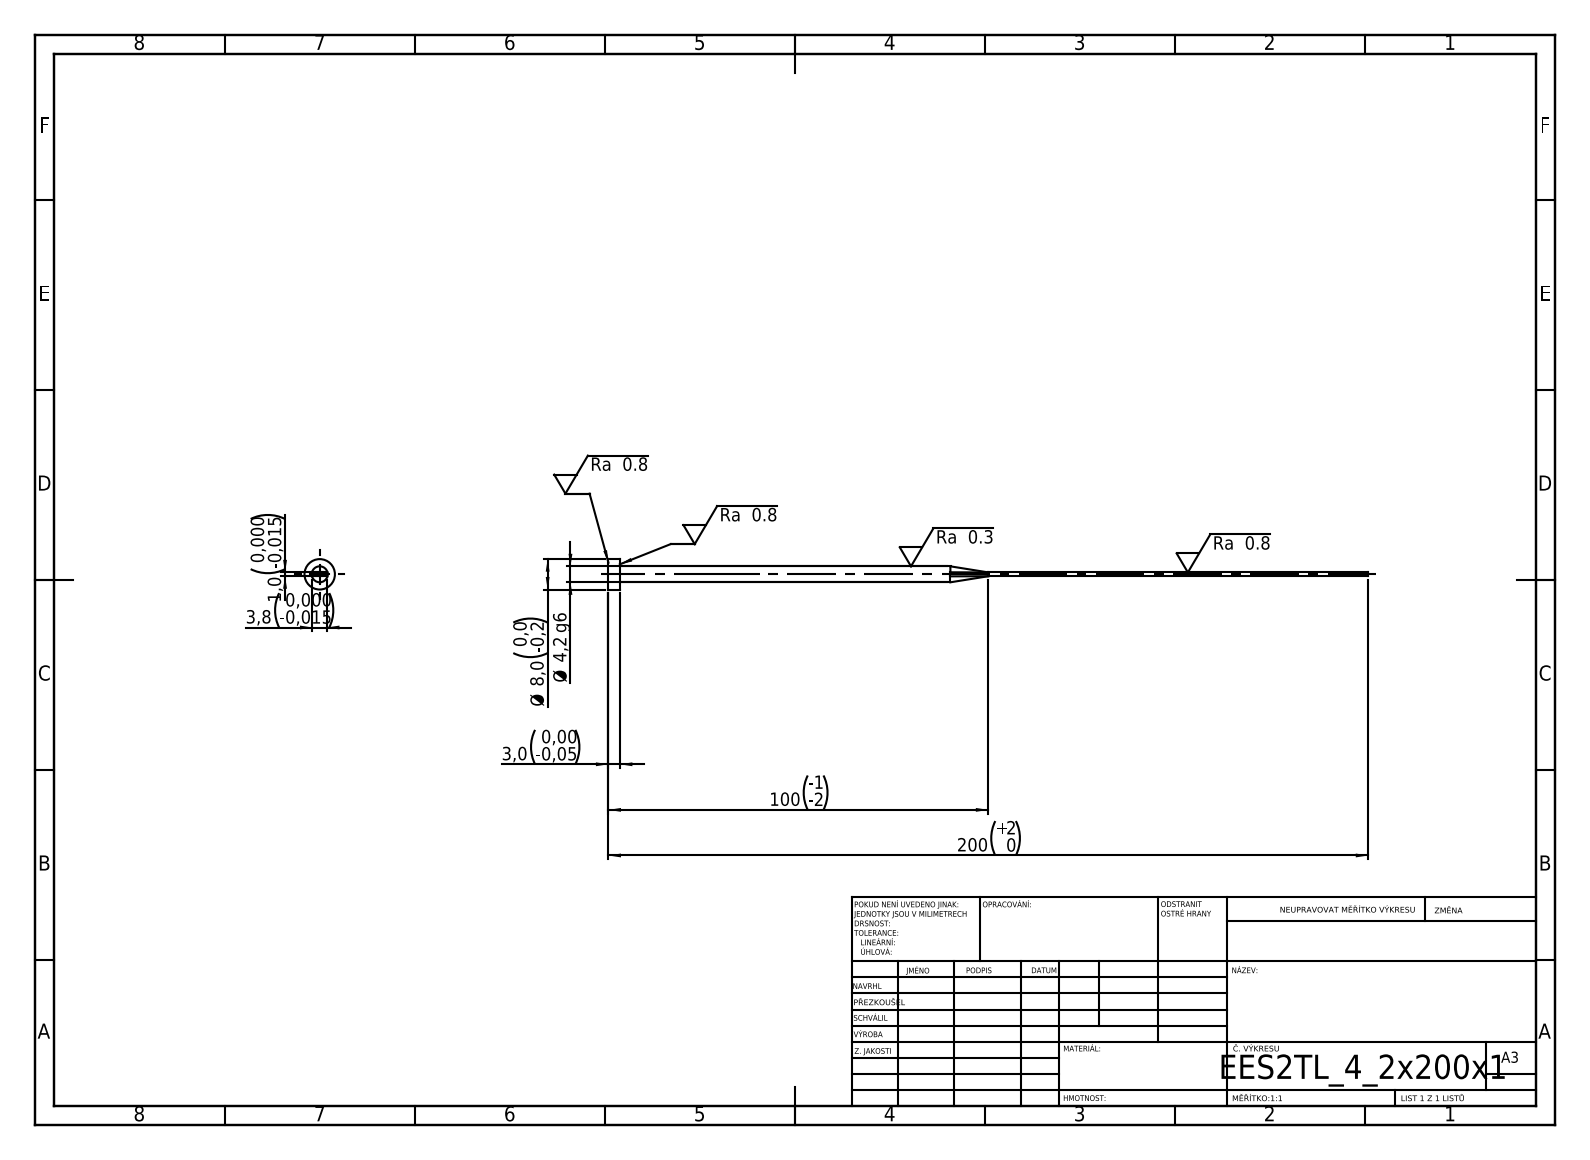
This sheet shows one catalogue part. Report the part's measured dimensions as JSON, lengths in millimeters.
{"step_written_by": "SolidWorks 2019 (CONFIG_CONTROL_DESIGN)", "units": "millimeters", "bodies": {"solids": 1, "faces": 15, "planar": 7, "cylindrical": 4, "other": 4}, "overall_size": [200, 8, 8], "volume_mm3": 1821, "surface_area_mm2": 2384, "round_bosses_or_shafts": [[8, 1], [4.2, 1]], "face_to_face_distances": [1, 3.8, 3, 200, 197]}
